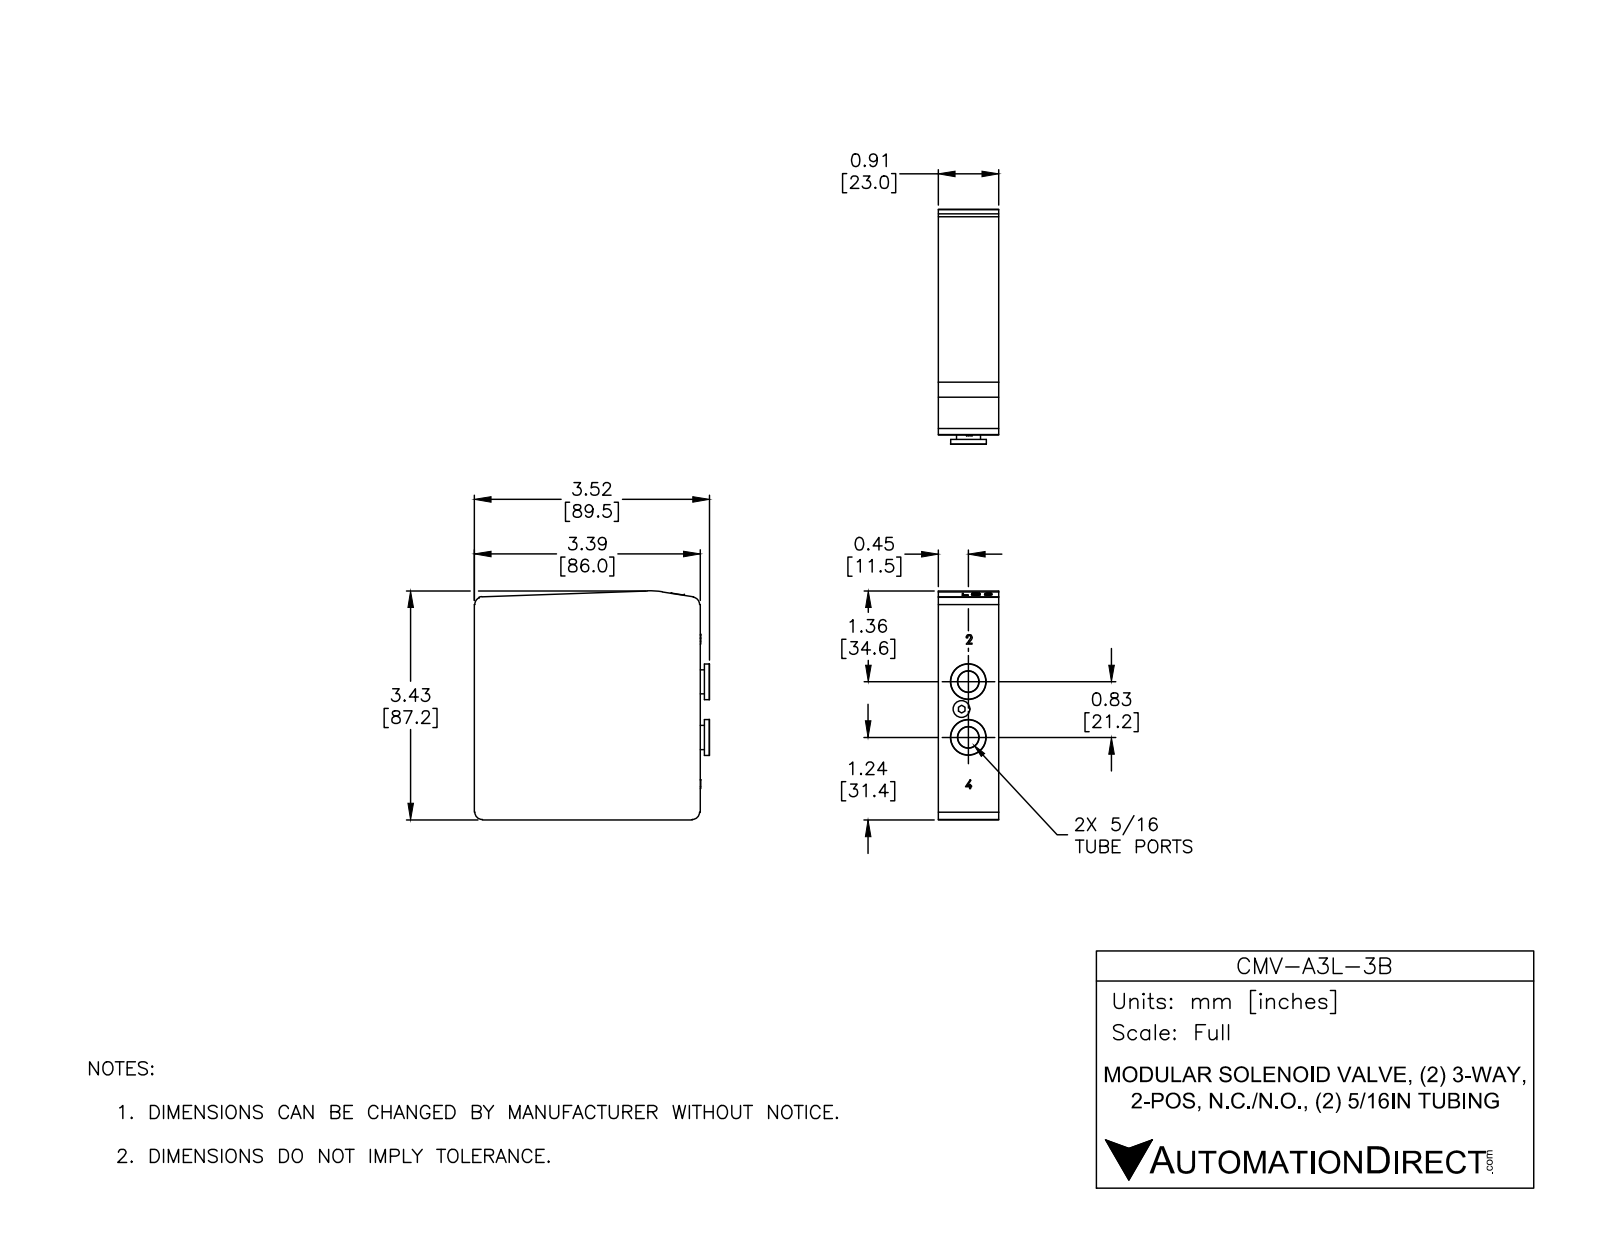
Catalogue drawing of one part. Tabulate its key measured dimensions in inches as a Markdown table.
| quantity | value |
| --- | --- |
| part name | CMV-A3L-3B |
| STEP written by | SolidWorks 2017 (AUTOMOTIVE_DESIGN) |
| units | inches |
| bodies | 1 solid, 156 faces (71 planar, 77 cylindrical, 8 other) |
| overall size | 3.524 × 3.434 × 0.906 |
| volume | 10.4 in³ |
| surface area | 36.19 in² |
| round holes (diameter × count) | 0.315 × 2, 0.252 × 1 |
| round bosses / shafts (diameter × count) | 0.535 × 2, 0.362 × 2 |
| partial cylindrical surfaces (radius × count) | 0.11 × 4, 0.044 × 2, 0.046 × 2, 0.054 × 2, 0.007 × 1, 0.022 × 1, 0.024 × 1, 0.024 × 1 |
| main face-to-face distances | 0.906, 3.386, 3.524, 0.138, 0.063, 3.449, 0.075, 3.378, 0.098, 0.071 |
| hole center spacings | 0.422, 0.437, 0.835 |
